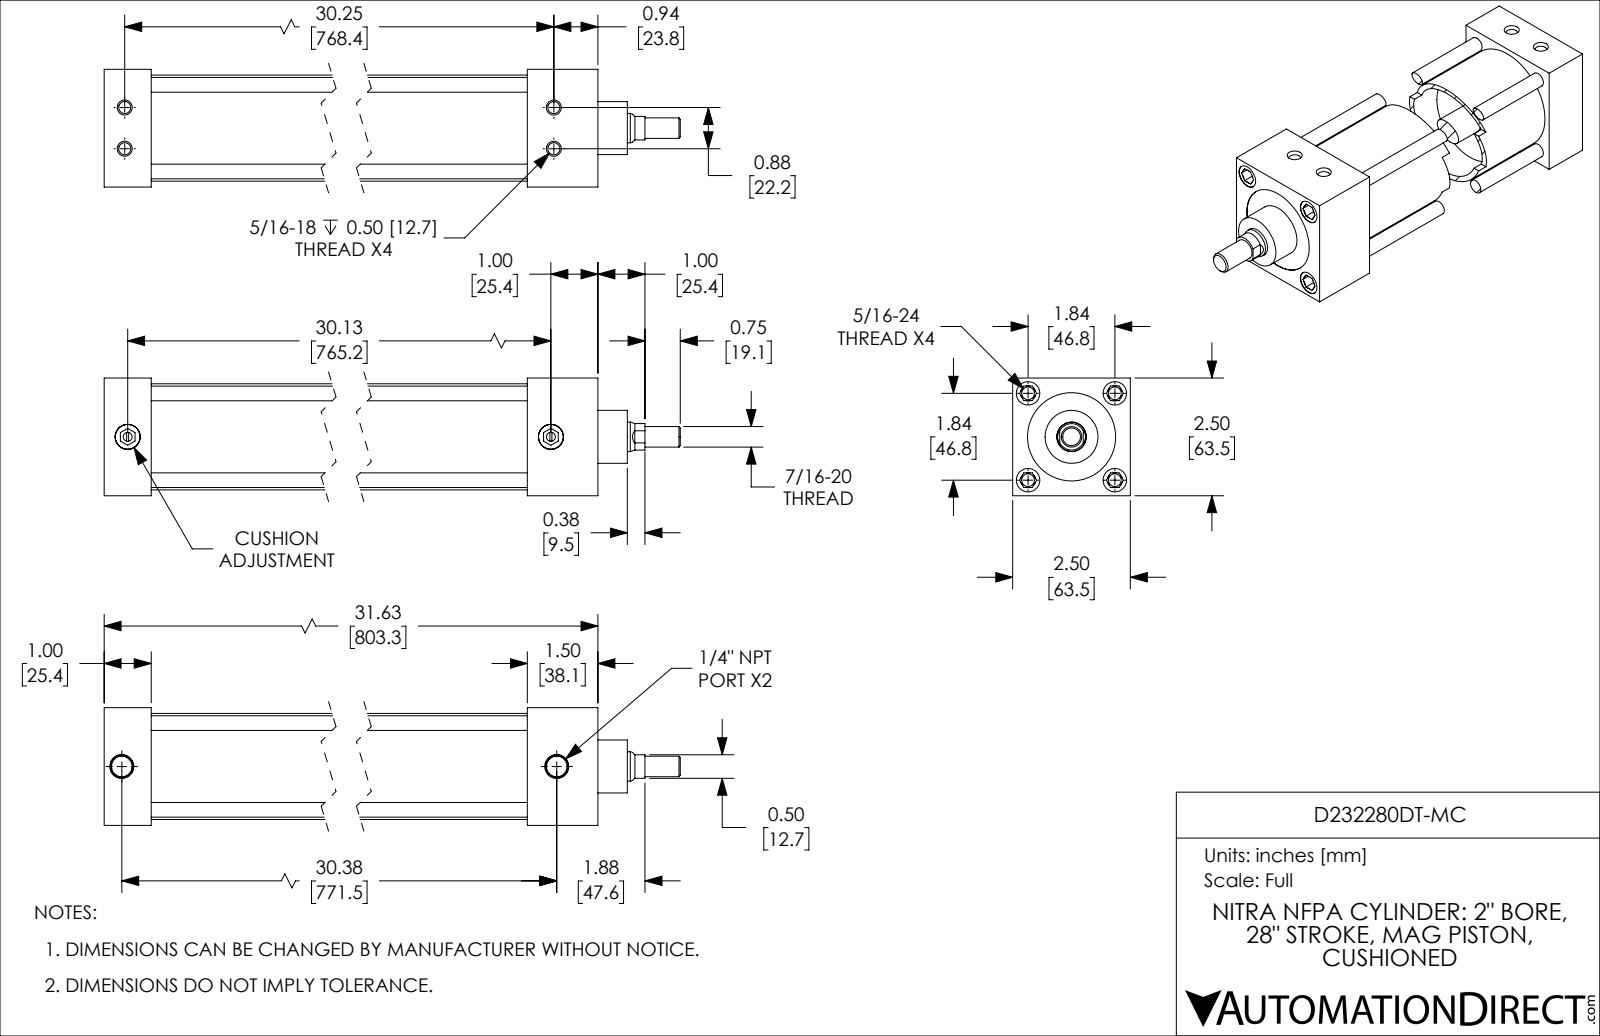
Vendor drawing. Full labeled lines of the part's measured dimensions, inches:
Part name (STEP PRODUCT): D232280DT-MC_BODY; D232280DT-MC_PISTON_KK1; D232280DT-MC; D232280DT-MC_CUSHION
STEP written by: SolidWorks 2019 (CONFIG_CONTROL_DESIGN)
Units: inches
Bodies: 4 solids, 248 faces (90 planar, 78 cylindrical, 80 other)
Overall size (bounding box): 33.375 × 2.5 × 2.5
Volume: 60.93 in³ · Surface area: 642.6 in²
Round holes (diameter × count): ⌀0.272 ×7, ⌀0.257 ×4, ⌀0.5 ×4, ⌀0.19 ×2, ⌀0.438 ×2, ⌀0.531 ×2, ⌀0.626 ×1, ⌀1.875 ×1, ⌀2.001 ×1
Round bosses / shafts (diameter × count): ⌀0.312 ×4, ⌀0.532 ×2, ⌀2.251 ×1, ⌀1.999 ×1, ⌀1.125 ×1, ⌀0.624 ×1, ⌀0.437 ×1
Partial cylindrical surfaces — rounded edges, fillets, slot ends (radius × count): R0.281 ×1
Main face-to-face distances: 2.5, 1, 30.125, 29.125, 1.125, 2.125, 28, 1.5, 31.625, 30.625
Hole centre spacings: 1.84, 1.844, 1.301, 0.441, 0.443, 0.875, 1.304, 2.602
